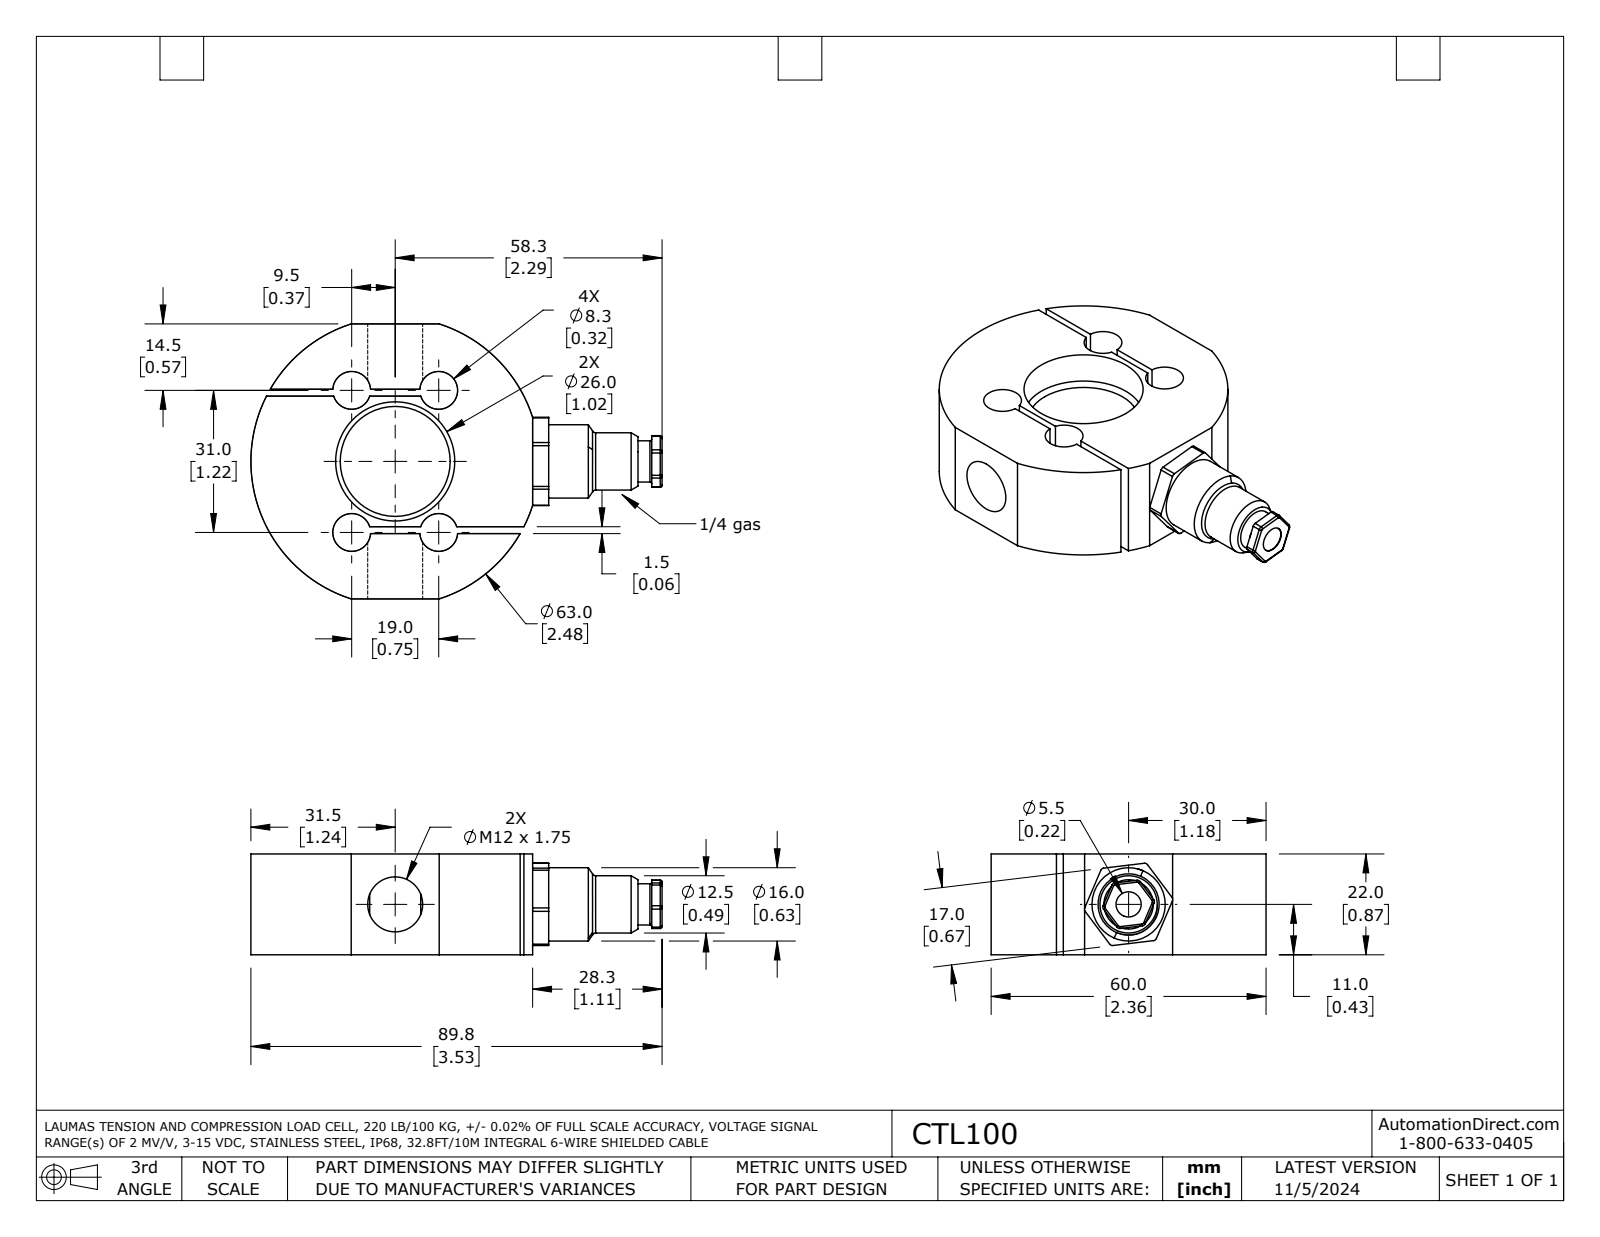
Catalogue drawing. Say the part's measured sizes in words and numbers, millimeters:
The part is named "CTL100". Its 3-D file was written by "SolidWorks 2021 (AUTOMOTIVE_DESIGN)". It is 2 solids with 114 faces: 39 planar, 56 cylindrical and 19 other. Overall it measures 89.7 by 60 by 22 millimeters. Its volume is 51 780 cubic millimeters and its surface area 18 170 square millimeters. Round holes: 4 of diameter 8.3, 1 of diameter 5.5, 1 of diameter 12, 1 of diameter 14, 1 of diameter 26. Round bosses or shafts: 1 of diameter 16, 1 of diameter 12.5, 1 of diameter 9. Partial cylindrical surfaces (rounded edges, fillets, slot ends): 12 of radius 0.8, 6 of radius 0.4, 1 of radius 31.5. The main face-to-face distances are 22, 8, 14, 1.5, 30, 14.2, 15.7, 44.2, 45.7, 28.5. The hole center spacings are 18.2, 19, 31, 36.3.
